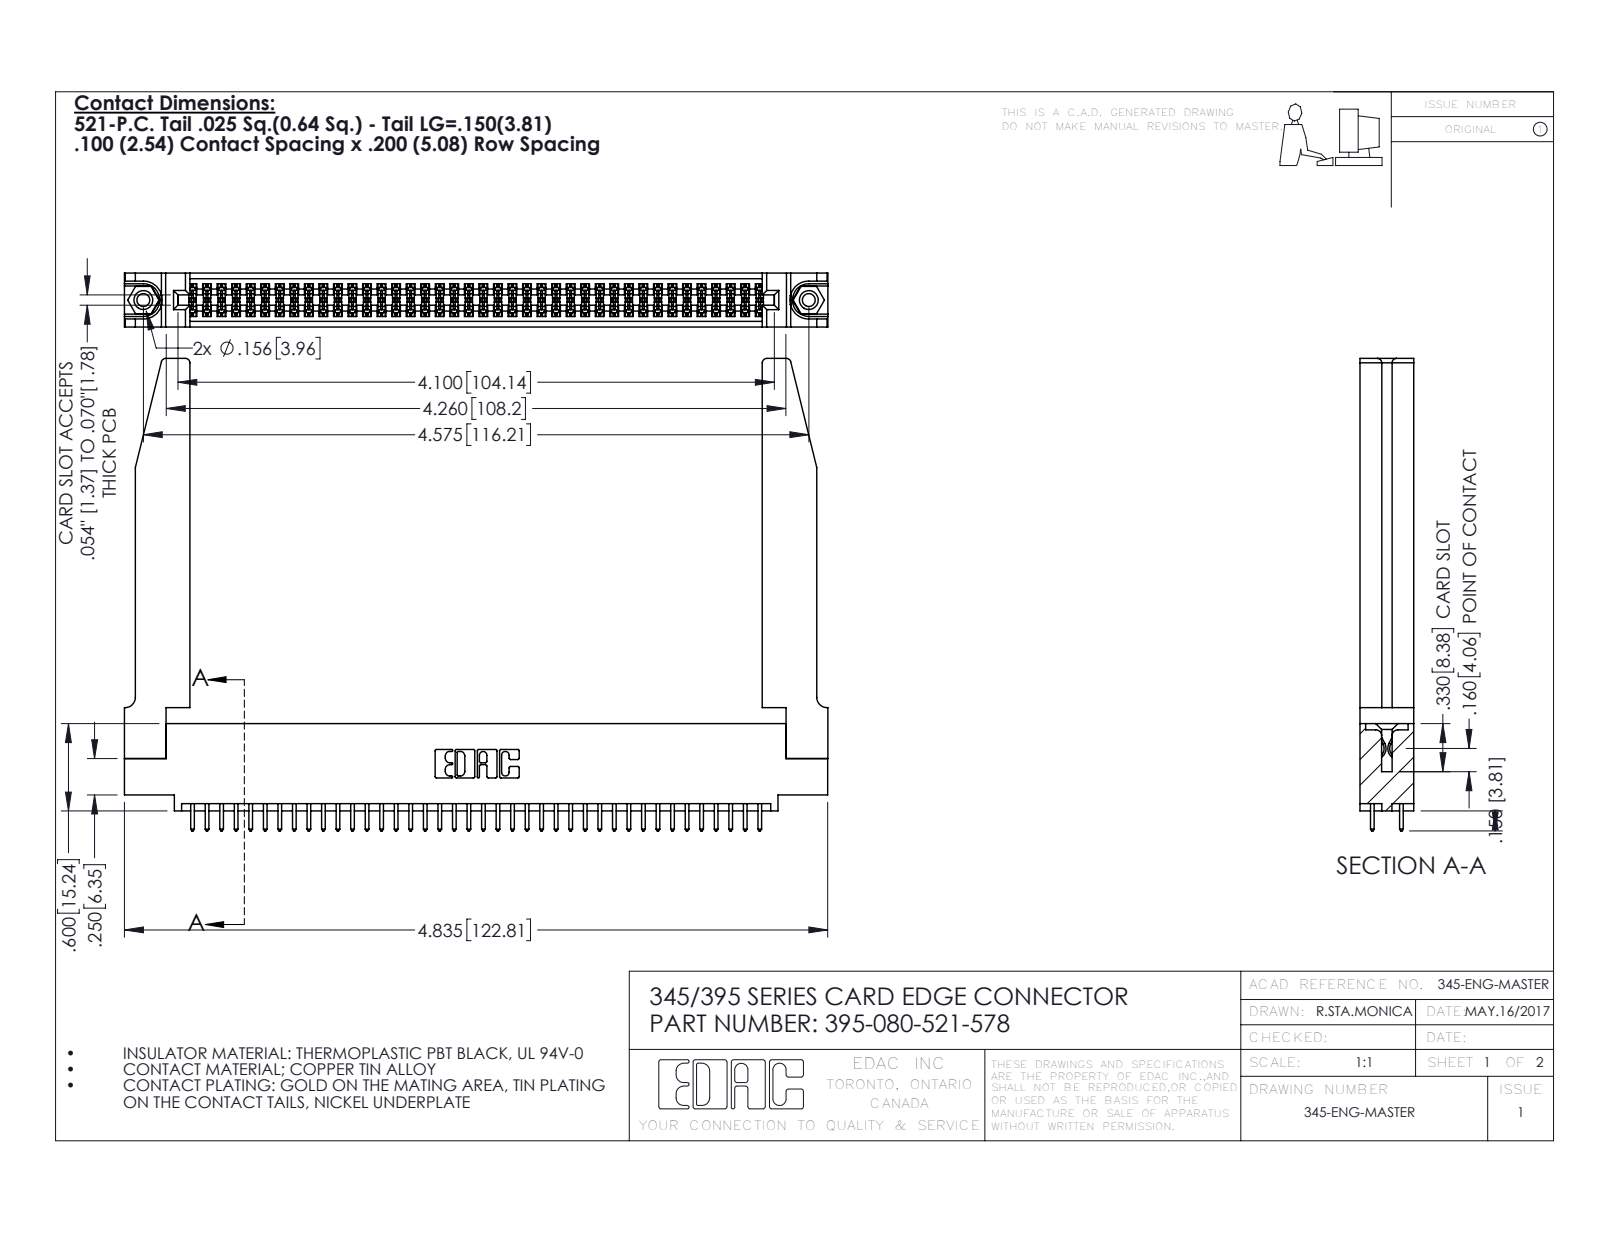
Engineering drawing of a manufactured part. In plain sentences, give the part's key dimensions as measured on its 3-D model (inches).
The part is named "395-080-521-578; 345-250-001_345-250-001-102; 345-292-001_345-293-121; 345-220-078_345-220-078 (+1 more)". Its 3-D file was written by "SolidWorks 2016 (CONFIG_CONTROL_DESIGN)". It is 85 solids with 4364 faces: 2866 planar, 1446 cylindrical and 52 other. Overall it measures 4.836 by 3.247 by 0.37 inches. Its volume is 1.195 cubic inches and its surface area 37.41 square inches. Round holes: 2 of diameter 0.089, 2 of diameter 0.125, 2 of diameter 0.156, 1 of diameter 0.064. Round bosses or shafts: 2 of diameter 0.155. Partial cylindrical surfaces (rounded edges, fillets, slot ends): 120 of radius 0.006, 80 of radius 0.01, 22 of radius 0.01, 8 of radius 0.03, 6 of radius 0.007, 6 of radius 0.031, 3 of radius 0.026, 2 of radius 0.014. The main face-to-face distances are 0.072, 0.37, 0.298, 0.2, 0.098, 0.272, 0.025, 0.225, 0.175, 0.148. The hole center spacings are 0.27, 4.339, 4.575.
